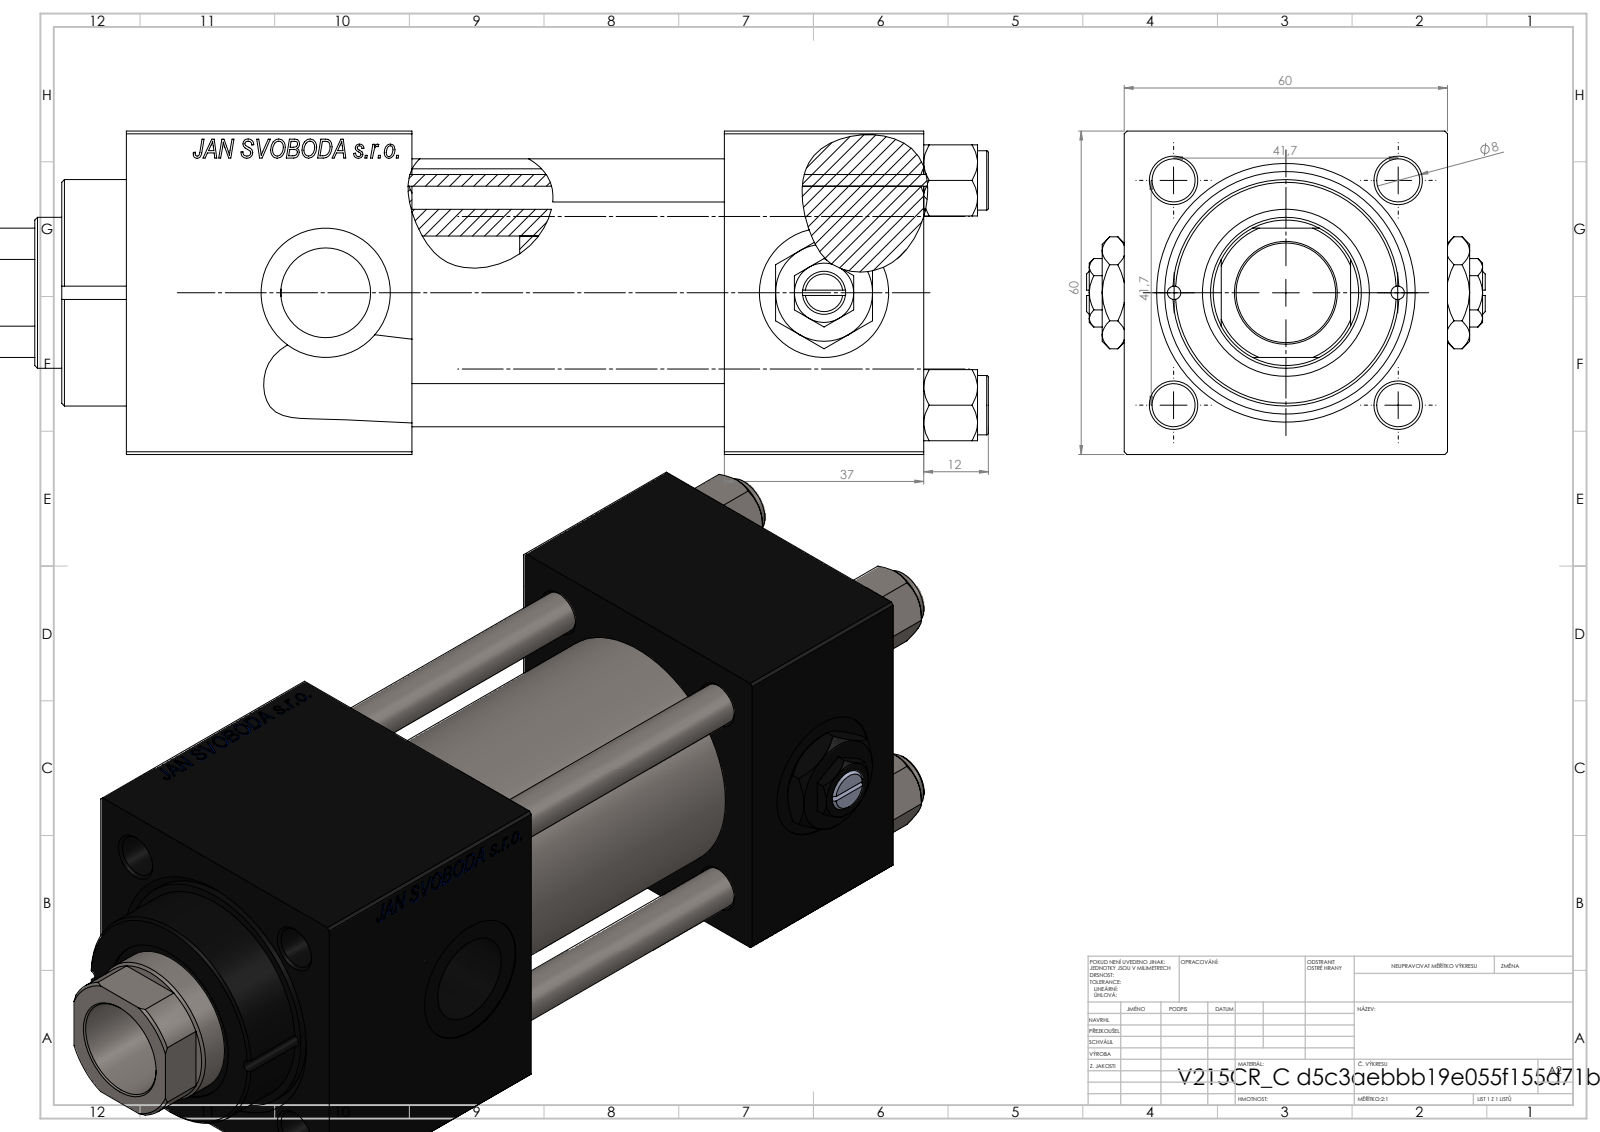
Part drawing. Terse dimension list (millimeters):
name: Zatka_pro_OIL_PORT; NUT_M5_C; V215CR_C_TYCINKA; V215CR_C_Body (+2 more)
written by: SolidWorks 2019 (CONFIG_CONTROL_DESIGN)
unit: mm
bodies: 13 solids, 1256 faces (576 planar, 102 cylindrical, 578 other)
size: 185 × 74 × 60
volume: 420 815 mm³; area: 114 475 mm²
holes: 4× ⌀8, 2× ⌀2.5, 2× ⌀7, 2× ⌀16.66, 2× ⌀24, 1× ⌀18.5, 1× ⌀28, 1× ⌀31, 1× ⌀40, 1× ⌀45
bosses: 4× ⌀11, 1× ⌀46, 1× ⌀42
rounds: 1× R13.5
face distances: 60, 37, 58, 95, 53, 119.3, 82.3, 24.3, 148, 111
hole spacings: 20.85, 29.49, 41.7, 46.53, 20.75, 58.97, 41.5, 92.5
